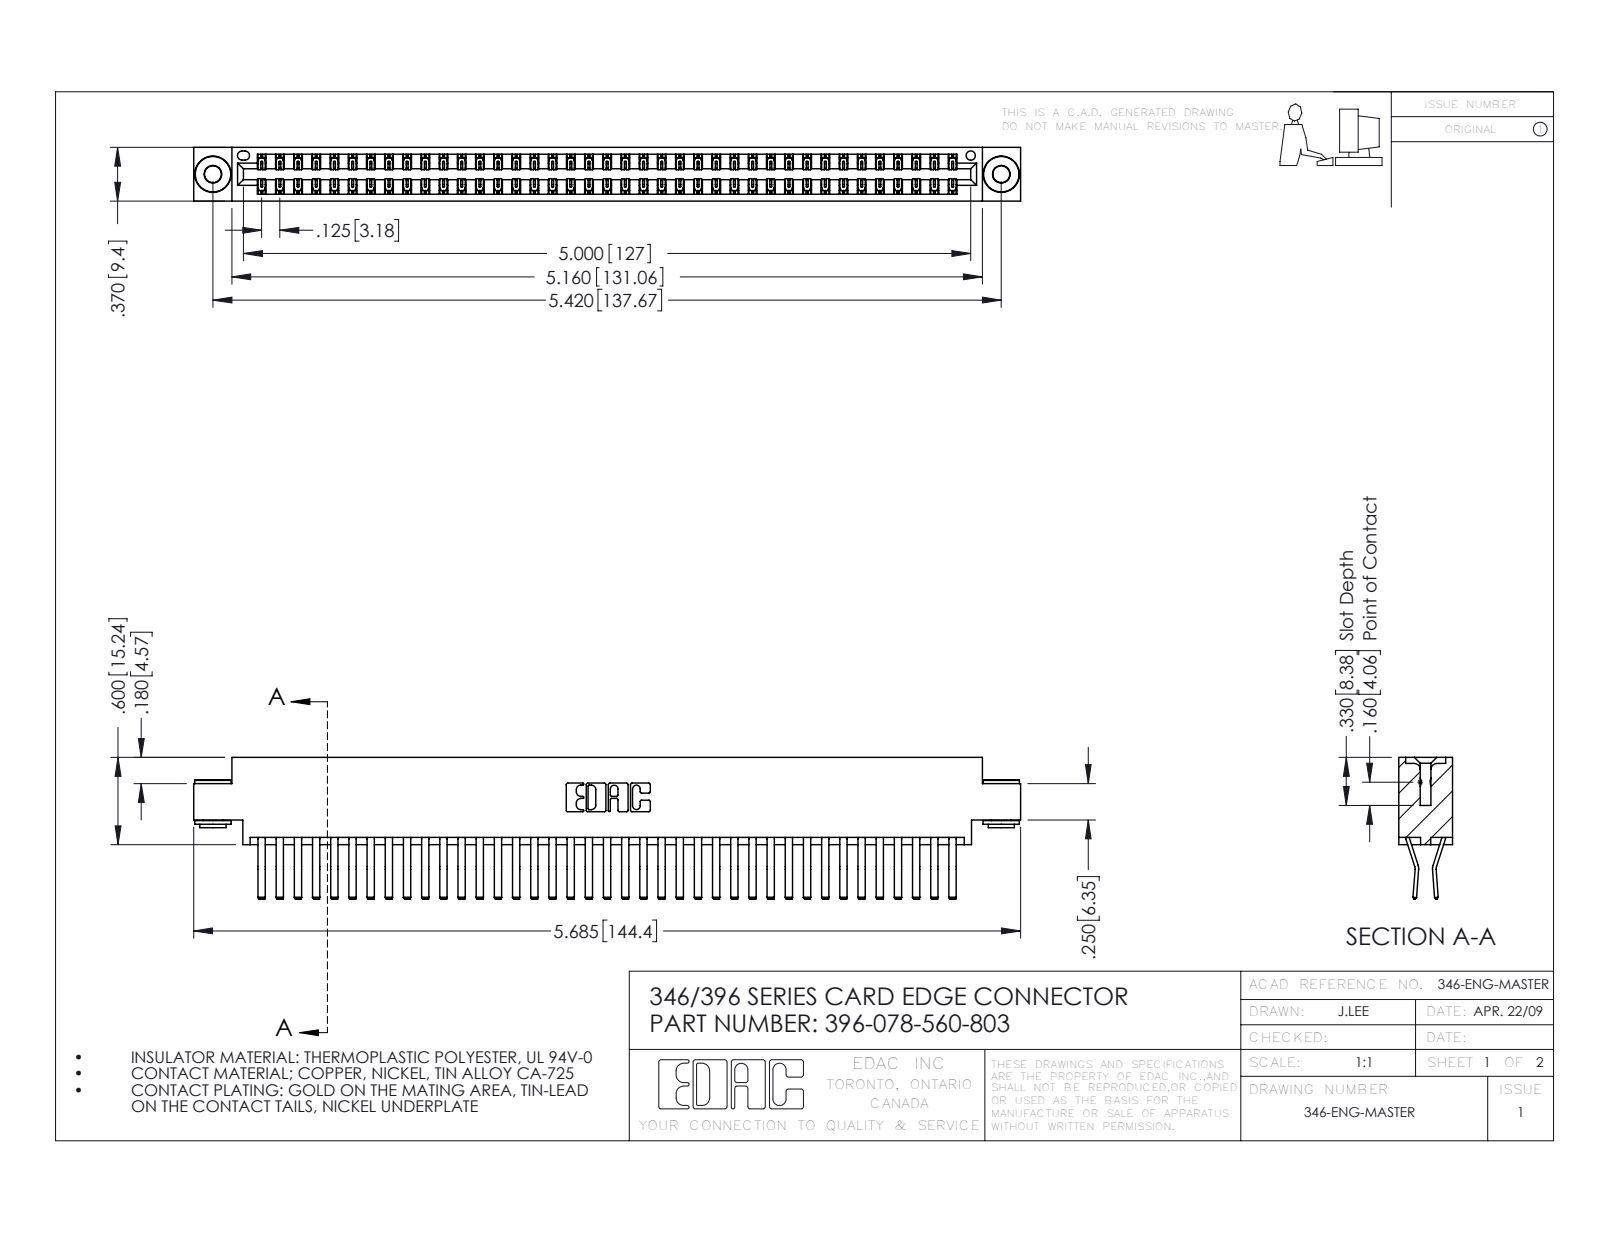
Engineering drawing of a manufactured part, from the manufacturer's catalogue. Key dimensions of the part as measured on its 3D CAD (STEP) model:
Part name (STEP PRODUCT): 345-250-002_345-250-002-102; 396-078-560-803; 345-292-001_560 Tail; 346 Part_0.170 Offset - 0.156 Dia-TH
STEP written by: SolidWorks 2016 (CONFIG_CONTROL_DESIGN)
Units: inches
Bodies: 81 solids, 4376 faces (2820 planar, 1548 cylindrical, 8 other)
Overall size (bounding box): 5.685 × 0.975 × 0.37
Volume: 0.881 in³ · Surface area: 33.4 in²
Round holes (diameter × count): ⌀0.116 ×2, ⌀0.156 ×2, ⌀0.064 ×1
Round bosses / shafts (diameter × count): ⌀0.25 ×2, ⌀0.18 ×2, ⌀0.136 ×2
Partial cylindrical surfaces — rounded edges, fillets, slot ends (radius × count): R0.006 ×117, R0.01 ×22, R0.007 ×6, R0.031 ×6, R0.026 ×3, R0.01 ×2, R0.014 ×2, R0.022 ×2
Main face-to-face distances: 0.048, 0.322, 0.37, 0.025, 0.25, 0.275, 0.072, 0.298, 0.148, 0.222
Hole centre spacings: 0.246, 5.211, 5.42
